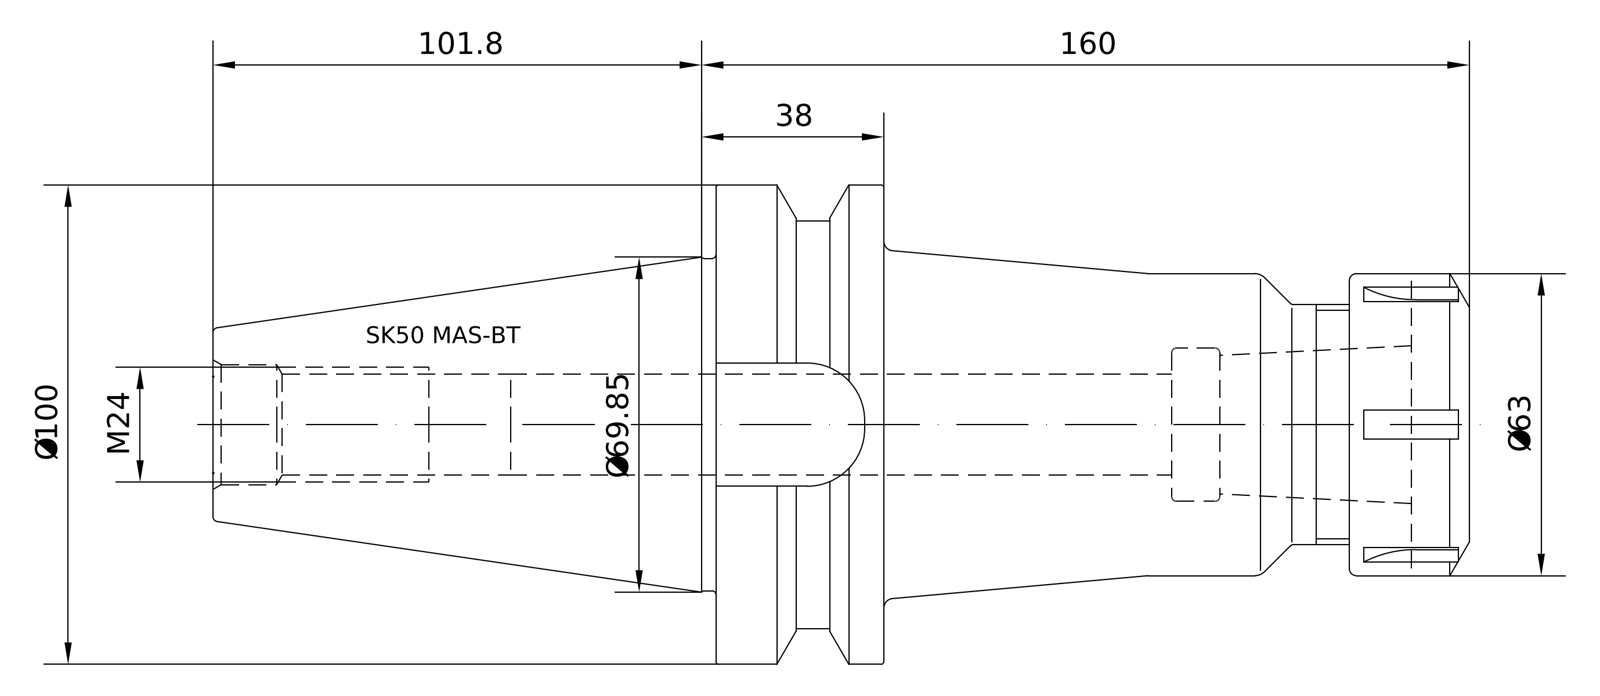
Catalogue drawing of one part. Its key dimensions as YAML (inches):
part_name: "50-522-40; 83-912-40; 50-522-40_ASM"
step_written_by: "PRO/ENGINEER BY PARAMETRIC TECHNOLOGY CORPORATION, 2010430 (CONFIG_CONTROL_DESIGN)"
units: inches
bodies: {solids: 2, faces: 150, planar: 54, cylindrical: 32, other: 64}
overall_size: [10.307, 3.936, 3.936]
volume: 50.75
surface_area: 132.3
round_holes:
  - {diameter: 0.817, count: 1}
  - {diameter: 0.985, count: 1}
  - {diameter: 1.012, count: 1}
  - {diameter: 1.201, count: 1}
round_bosses_or_shafts:
  - {diameter: 3.936, count: 1}
  - {diameter: 3.337, count: 1}
  - {diameter: 2.722, count: 1}
  - {diameter: 2.48, count: 1}
  - {diameter: 1.969, count: 1}
  - {diameter: 0.945, count: 1}
partial_cylinders:
  - {radius: 0.106, count: 6}
  - {radius: 0.508, count: 1}
face_to_face_distances: [3.799, 1.378, 5.177, 6.181, 4.803, 1.004, 2.772, 4.098, 2.72, 1.079]
